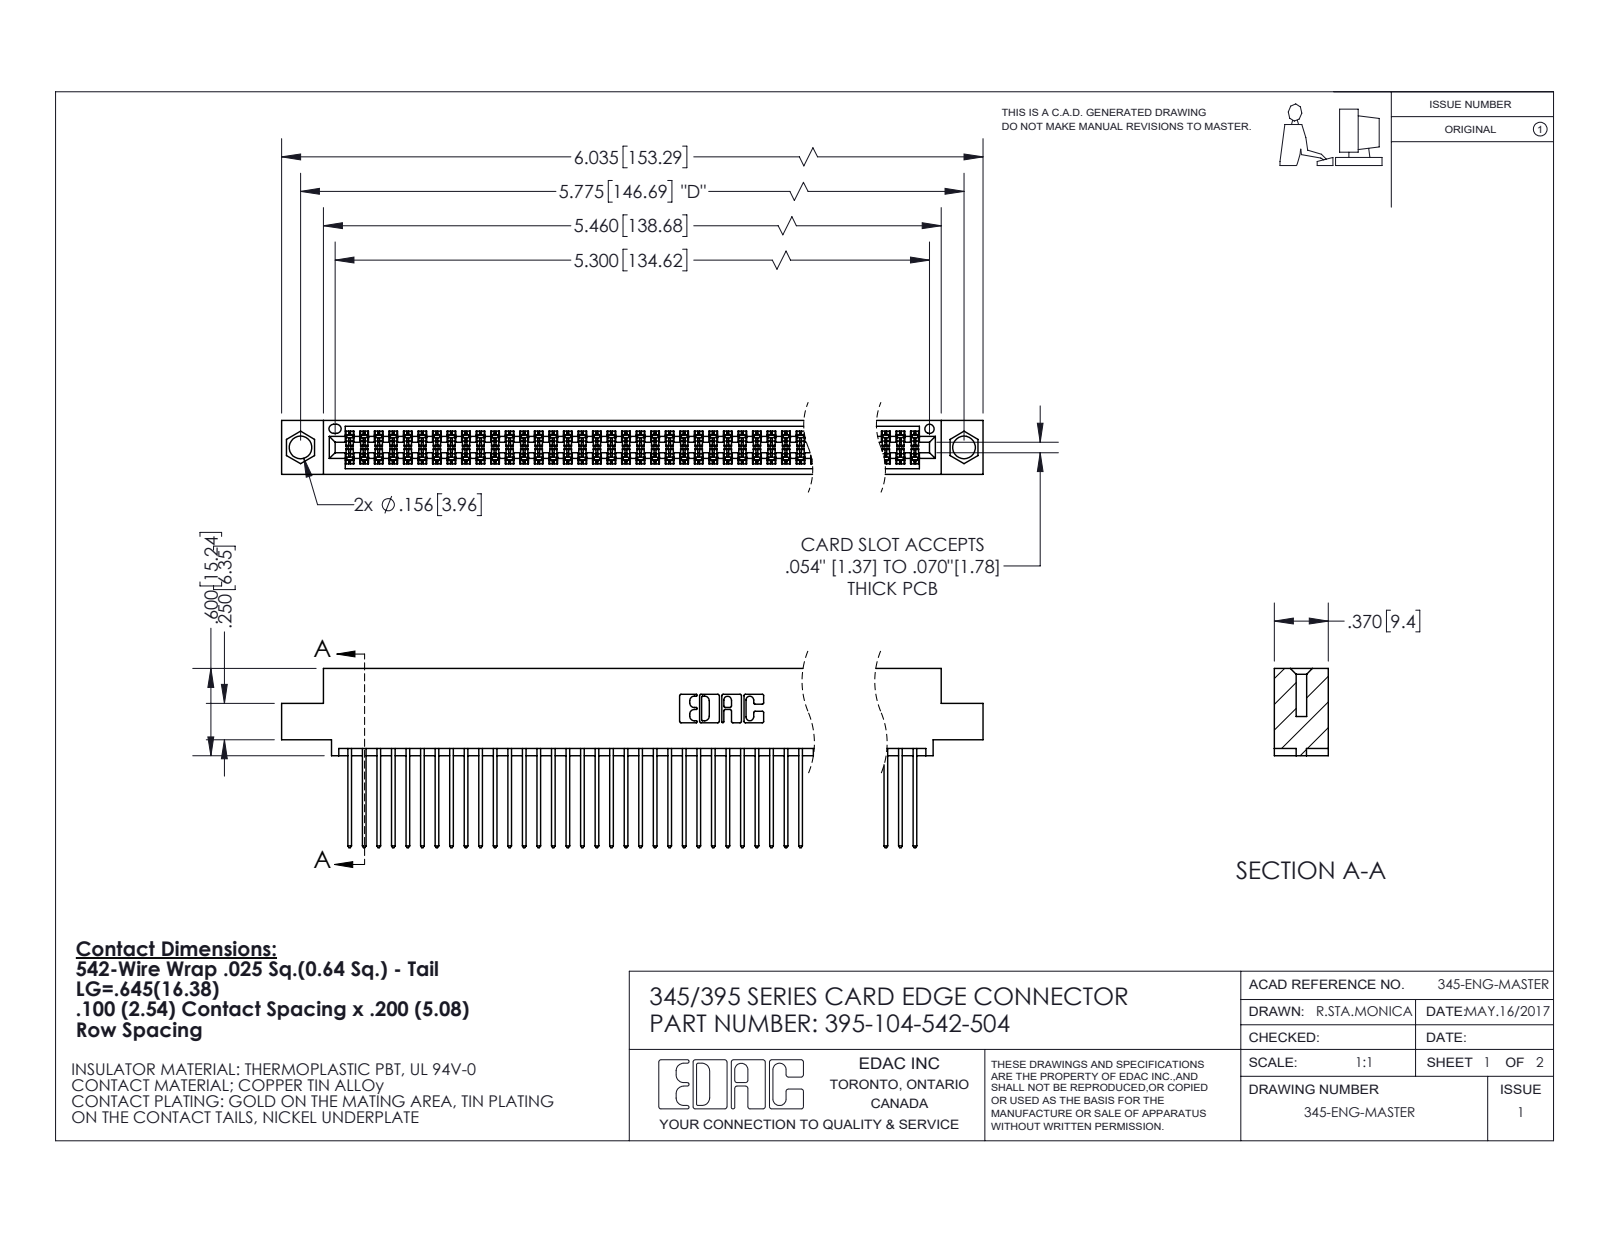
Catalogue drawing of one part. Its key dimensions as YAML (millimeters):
part_name: "345 Part_0.110 Offset - 0.156 Dia-TI; 345-292-001_345-293-142; 395-104-542-504"
step_written_by: "SolidWorks 2020 (CONFIG_CONTROL_DESIGN)"
units: millimeters
bodies: {solids: 105, faces: 5344, planar: 3530, cylindrical: 1814, other: 0}
overall_size: [153.3, 31.3, 9.4]
volume: 15300
surface_area: 25010
round_holes:
  - {diameter: 4, count: 2}
  - {diameter: 1.6, count: 1}
partial_cylinders:
  - {radius: 0.2, count: 207}
  - {radius: 0.3, count: 104}
  - {radius: 0.3, count: 22}
  - {radius: 0.2, count: 6}
  - {radius: 0.8, count: 6}
  - {radius: 0.7, count: 3}
  - {radius: 0.4, count: 2}
  - {radius: 0.5, count: 2}
face_to_face_distances: [7.6, 1.8, 5.1, 2.5, 6.9, 0.6, 5.7, 9.4, 4.4, 3.8]
hole_center_spacings: [6.9, 140.7, 146.7]
